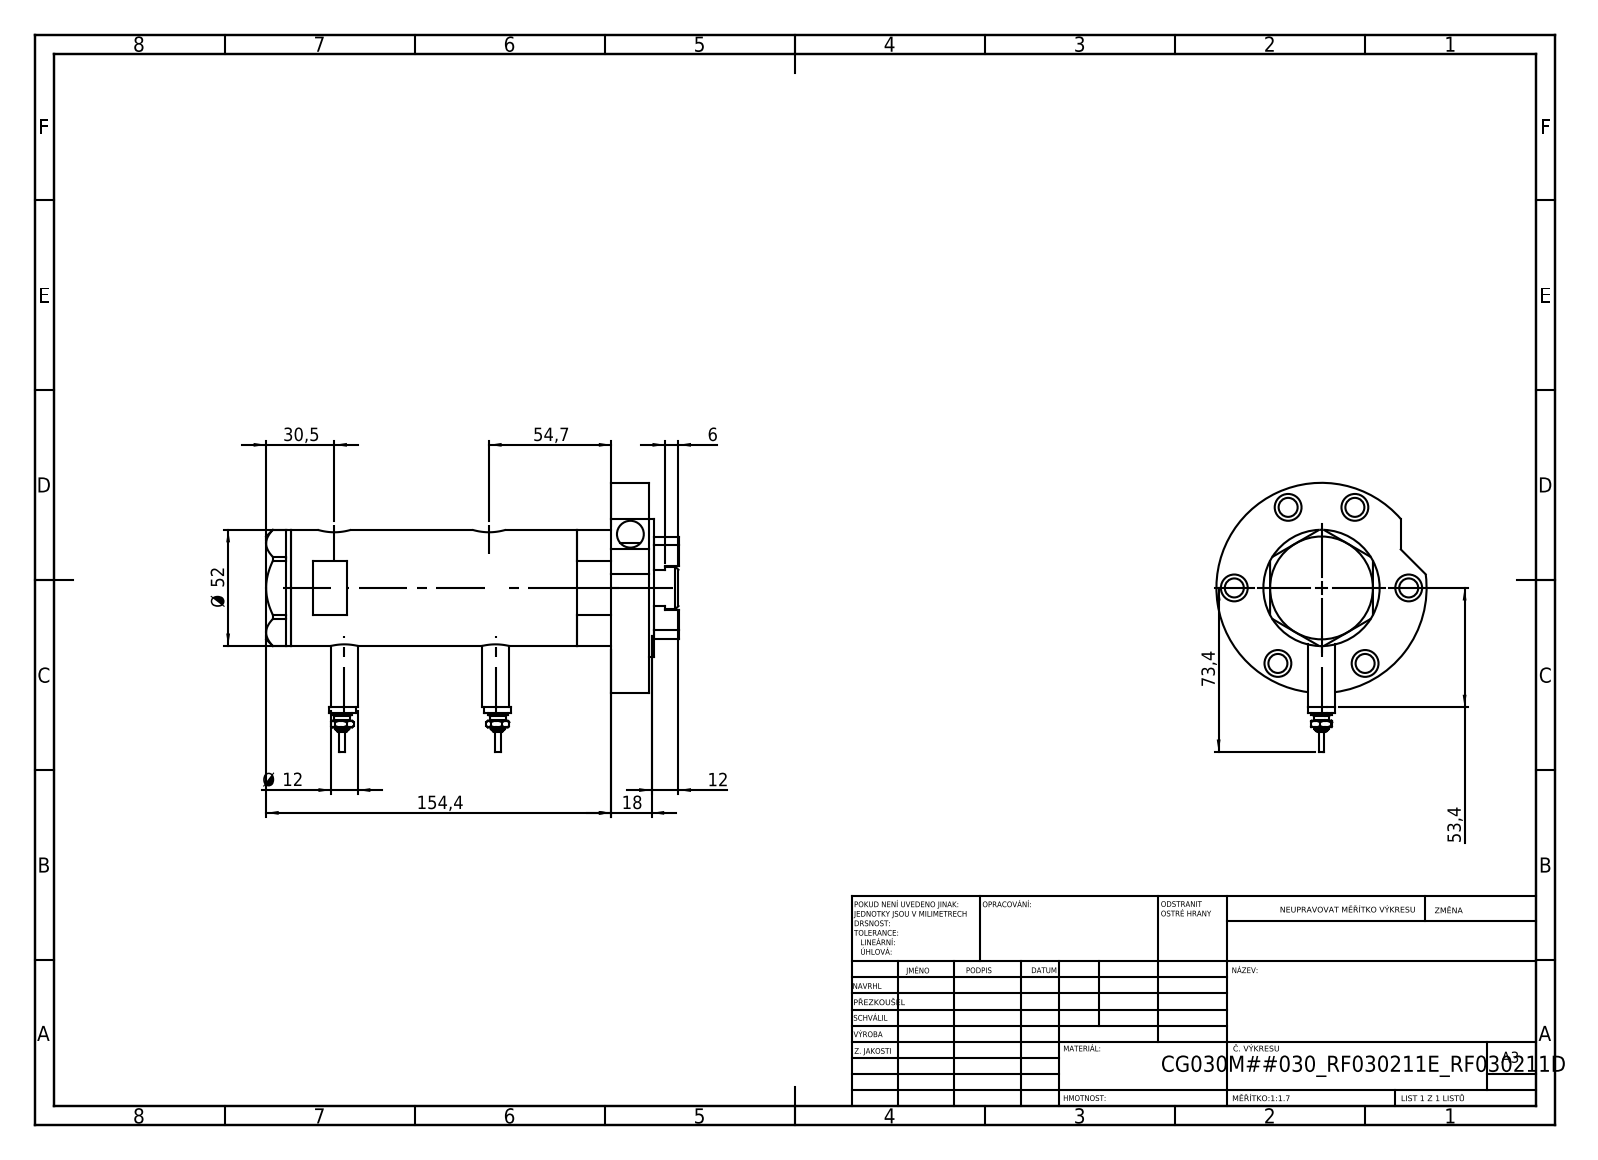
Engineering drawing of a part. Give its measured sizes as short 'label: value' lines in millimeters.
name: V270CG_FRONT; V270CG_RF211D; V270CG_RF211E; V270CG_MIDDLE (+3 more)
written by: SolidWorks 2019 (CONFIG_CONTROL_DESIGN)
unit: mm
bodies: 9 solids, 310 faces (128 planar, 118 cylindrical, 64 other)
size: 184.6 × 120.4 × 94
volume: 427 023 mm³; area: 107 113 mm²
holes: 7× ⌀12, 6× ⌀8.5, 4× ⌀5.1, 4× ⌀9, 2× ⌀9.73, 2× ⌀12.5, 2× ⌀15, 1× ⌀6.5, 1× ⌀20, 1× ⌀21.5, 1× ⌀30, 1× ⌀33
bosses: 4× ⌀12, 2× ⌀9, 2× ⌀7, 2× ⌀4.5, 2× ⌀2.5, 1× ⌀94, 1× ⌀62, 1× ⌀52
face distances: 17, 143.4, 160.4, 2, 11, 162.4, 91.5, 51.9, 68.9, 173.4
hole spacings: 39, 16.74, 37.57, 46.81, 10, 22.37, 22.95, 28.26
